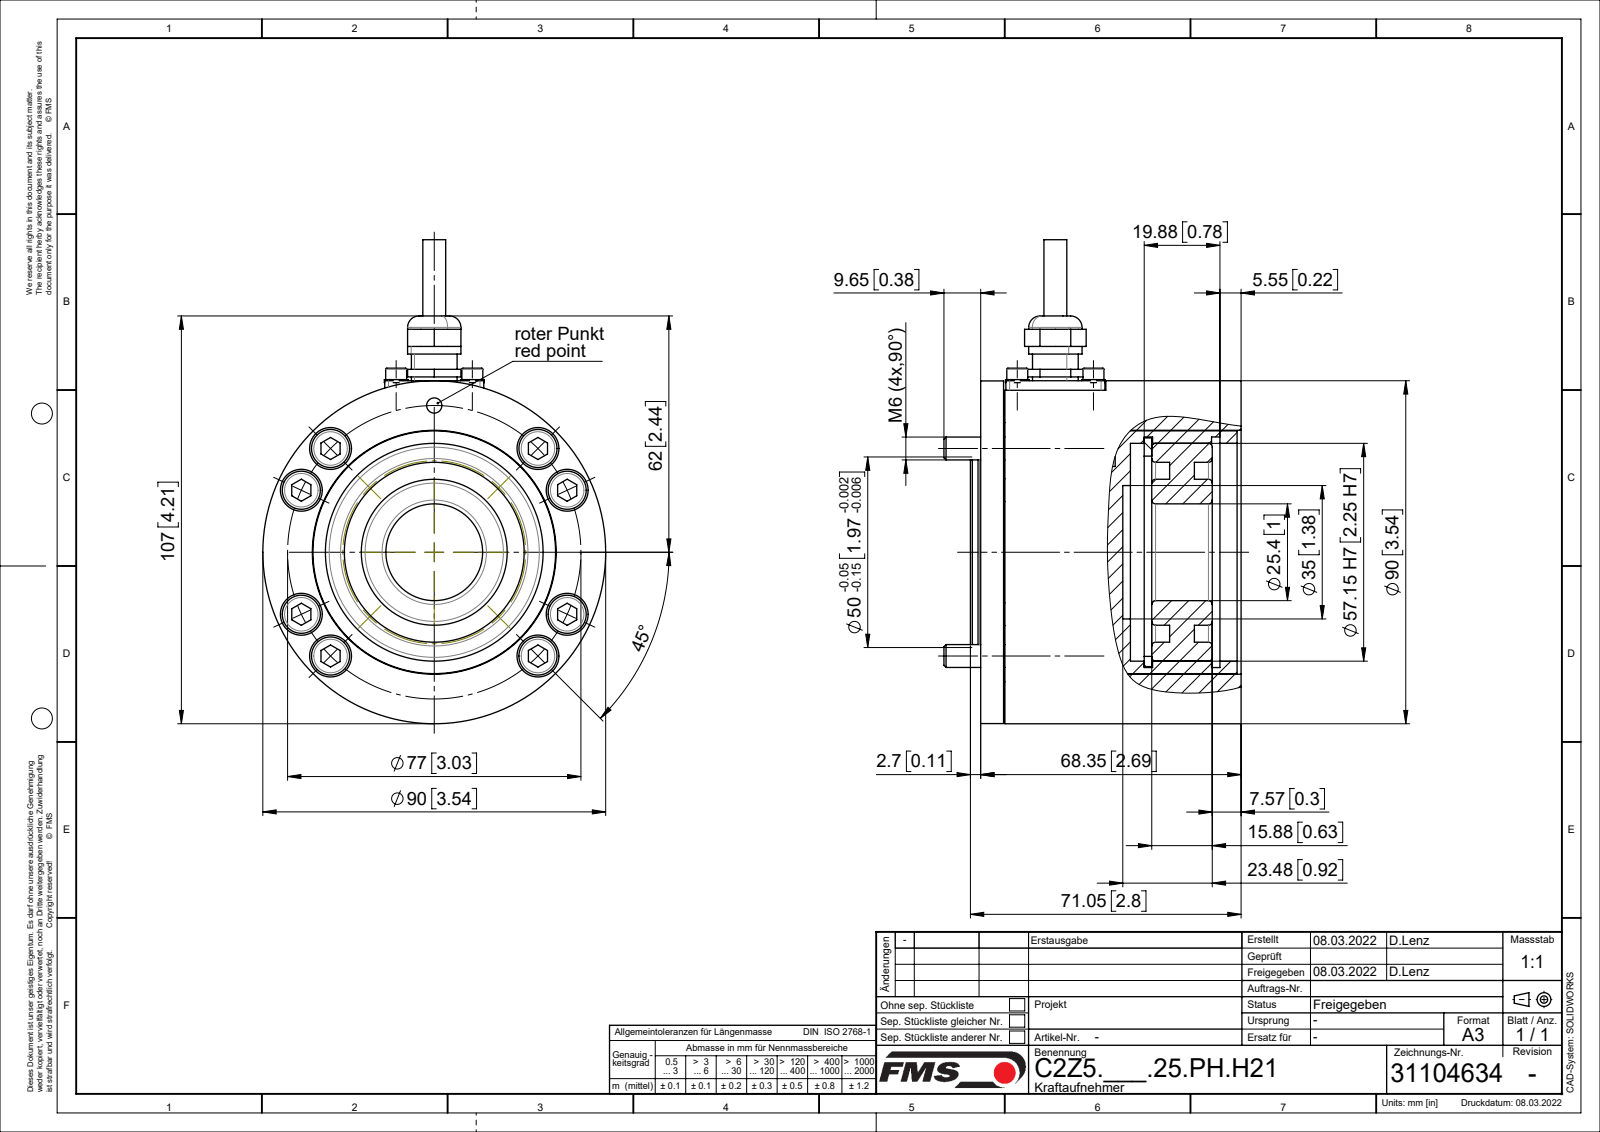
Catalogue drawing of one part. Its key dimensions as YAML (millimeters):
part_name: "Zyl-Schr DIN912_M3x6; 31104488_01; 51283_01; 31104496_stp_01 (+8 more)"
step_written_by: "SolidWorks 2018 (CONFIG_CONTROL_DESIGN)"
units: millimeters
bodies: {solids: 24, faces: 556, planar: 222, cylindrical: 232, other: 102}
overall_size: [127, 90, 78]
volume: 296468
surface_area: 118599
round_holes:
  - {diameter: 6.5, count: 8}
  - {diameter: 11, count: 8}
  - {diameter: 2.5, count: 6}
  - {diameter: 3.1, count: 4}
  - {diameter: 3.4, count: 4}
  - {diameter: 5, count: 4}
  - {diameter: 7, count: 4}
  - {diameter: 4, count: 2}
  - {diameter: 6, count: 1}
  - {diameter: 10.2, count: 1}
  - {diameter: 12.2, count: 1}
  - {diameter: 18, count: 1}
round_bosses_or_shafts:
  - {diameter: 10, count: 8}
  - {diameter: 6, count: 8}
  - {diameter: 6.2, count: 4}
  - {diameter: 5.5, count: 4}
  - {diameter: 3, count: 4}
  - {diameter: 90, count: 1}
  - {diameter: 89.9, count: 1}
  - {diameter: 63.7, count: 1}
partial_cylinders:
  - {radius: 0.1, count: 4}
  - {radius: 1, count: 4}
  - {radius: 4.16, count: 2}
  - {radius: 5, count: 2}
  - {radius: 23.2, count: 1}
  - {radius: 26.29, count: 1}
face_to_face_distances: [6, 3.3, 2.7, 33.05, 32, 38, 30, 29.3, 35.3, 28.95]
hole_center_spacings: [20, 38.5, 13.37, 14.14, 38.49, 44.16, 54.44, 63.07]
